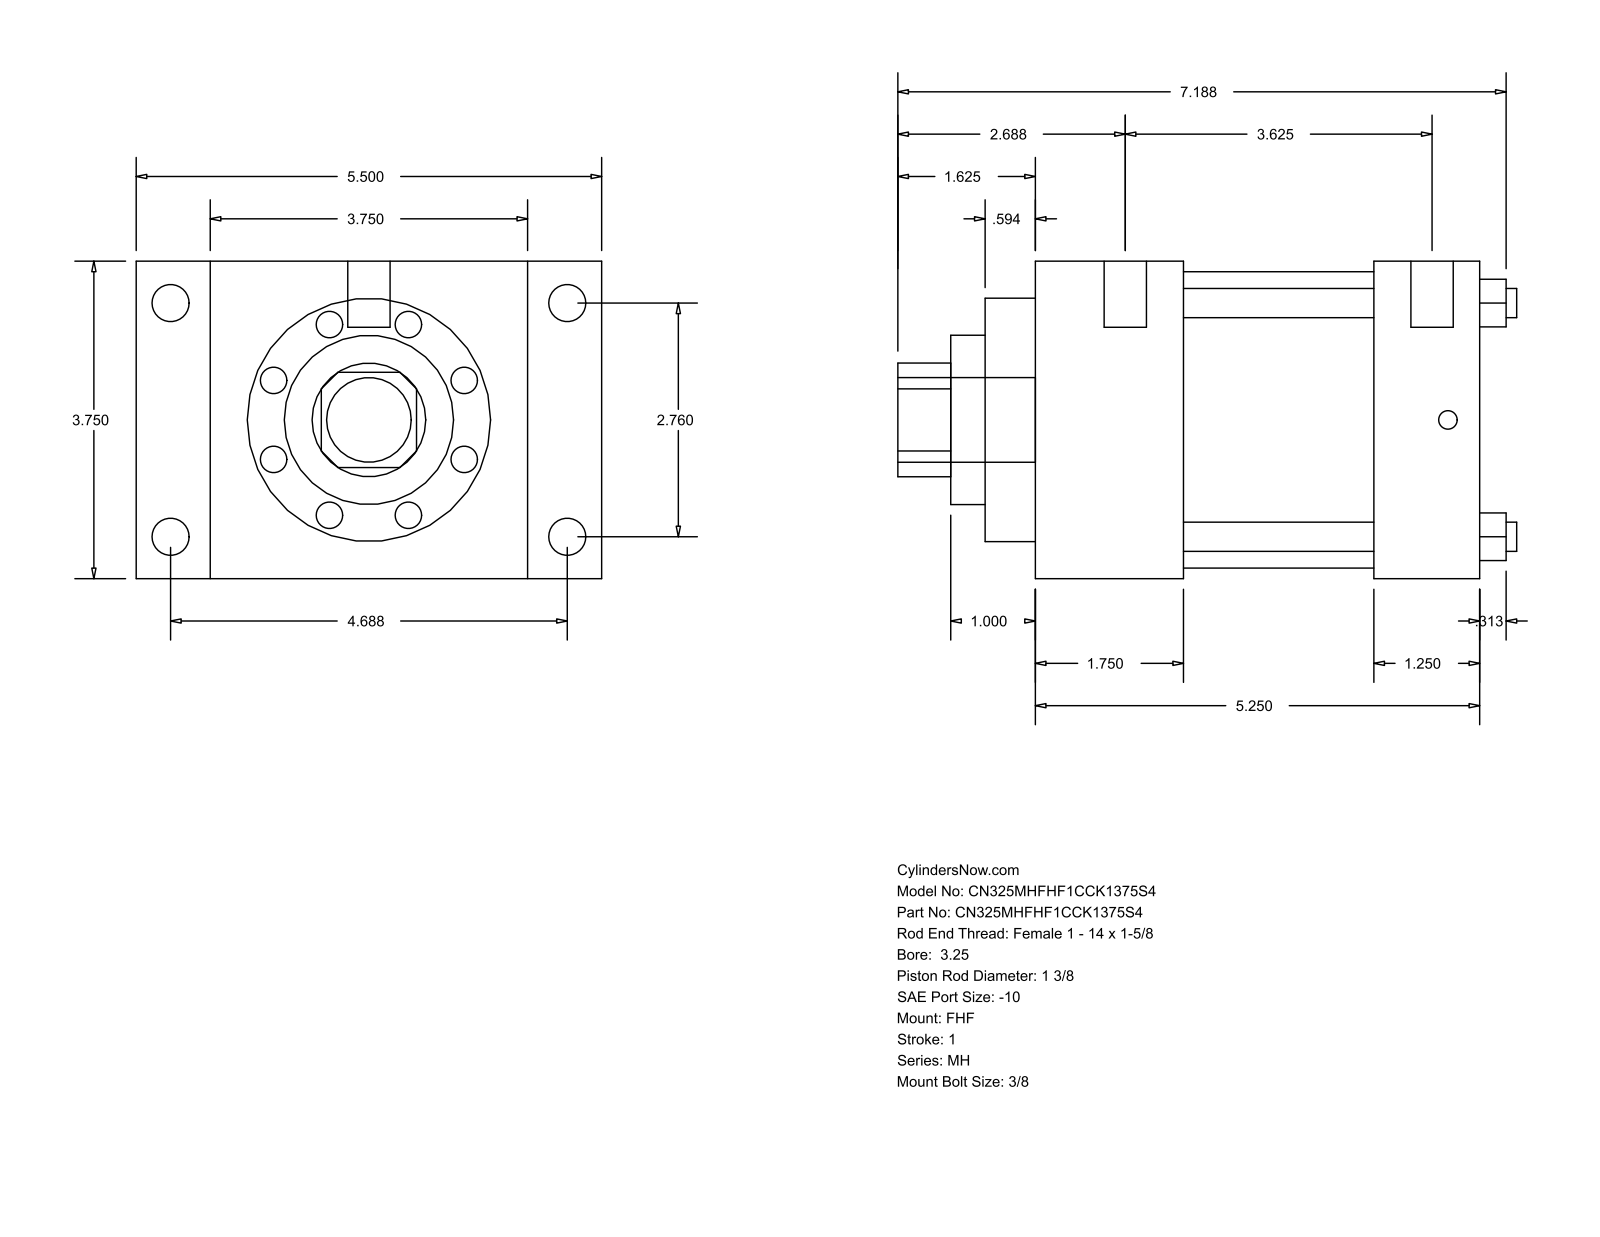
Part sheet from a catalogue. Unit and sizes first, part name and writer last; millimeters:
Units: millimetres
Overall size (bounding box): 185.74 × 139.7 × 95.25
Round holes (diameter × count): ⌀8.76 ×4, ⌀34.92 ×1, ⌀50.8 ×1, ⌀73.03 ×1, ⌀88.9 ×1
Round bosses / shafts (diameter × count): ⌀11.13 ×4, ⌀5.56 ×4, ⌀12.7 ×2, ⌀25.4 ×1
Partial cylindrical surfaces — rounded edges, fillets, slot ends (radius × count): R17.06 ×1
Main face-to-face distances: 95.24, 133.35, 44.45, 88.9, 22.23, 117.47, 139.7, 101.61, 57.16, 31.74
Hole centre spacings: 49.57, 70.1, 99.14
Bodies: 0 solids, 90 faces (61 planar, 29 cylindrical, 0 other)
Part name (STEP PRODUCT): MH_FHF__0325_1.375
STEP written by: GSSL Pune (CONFIG_CONTROL_DESIGN)
